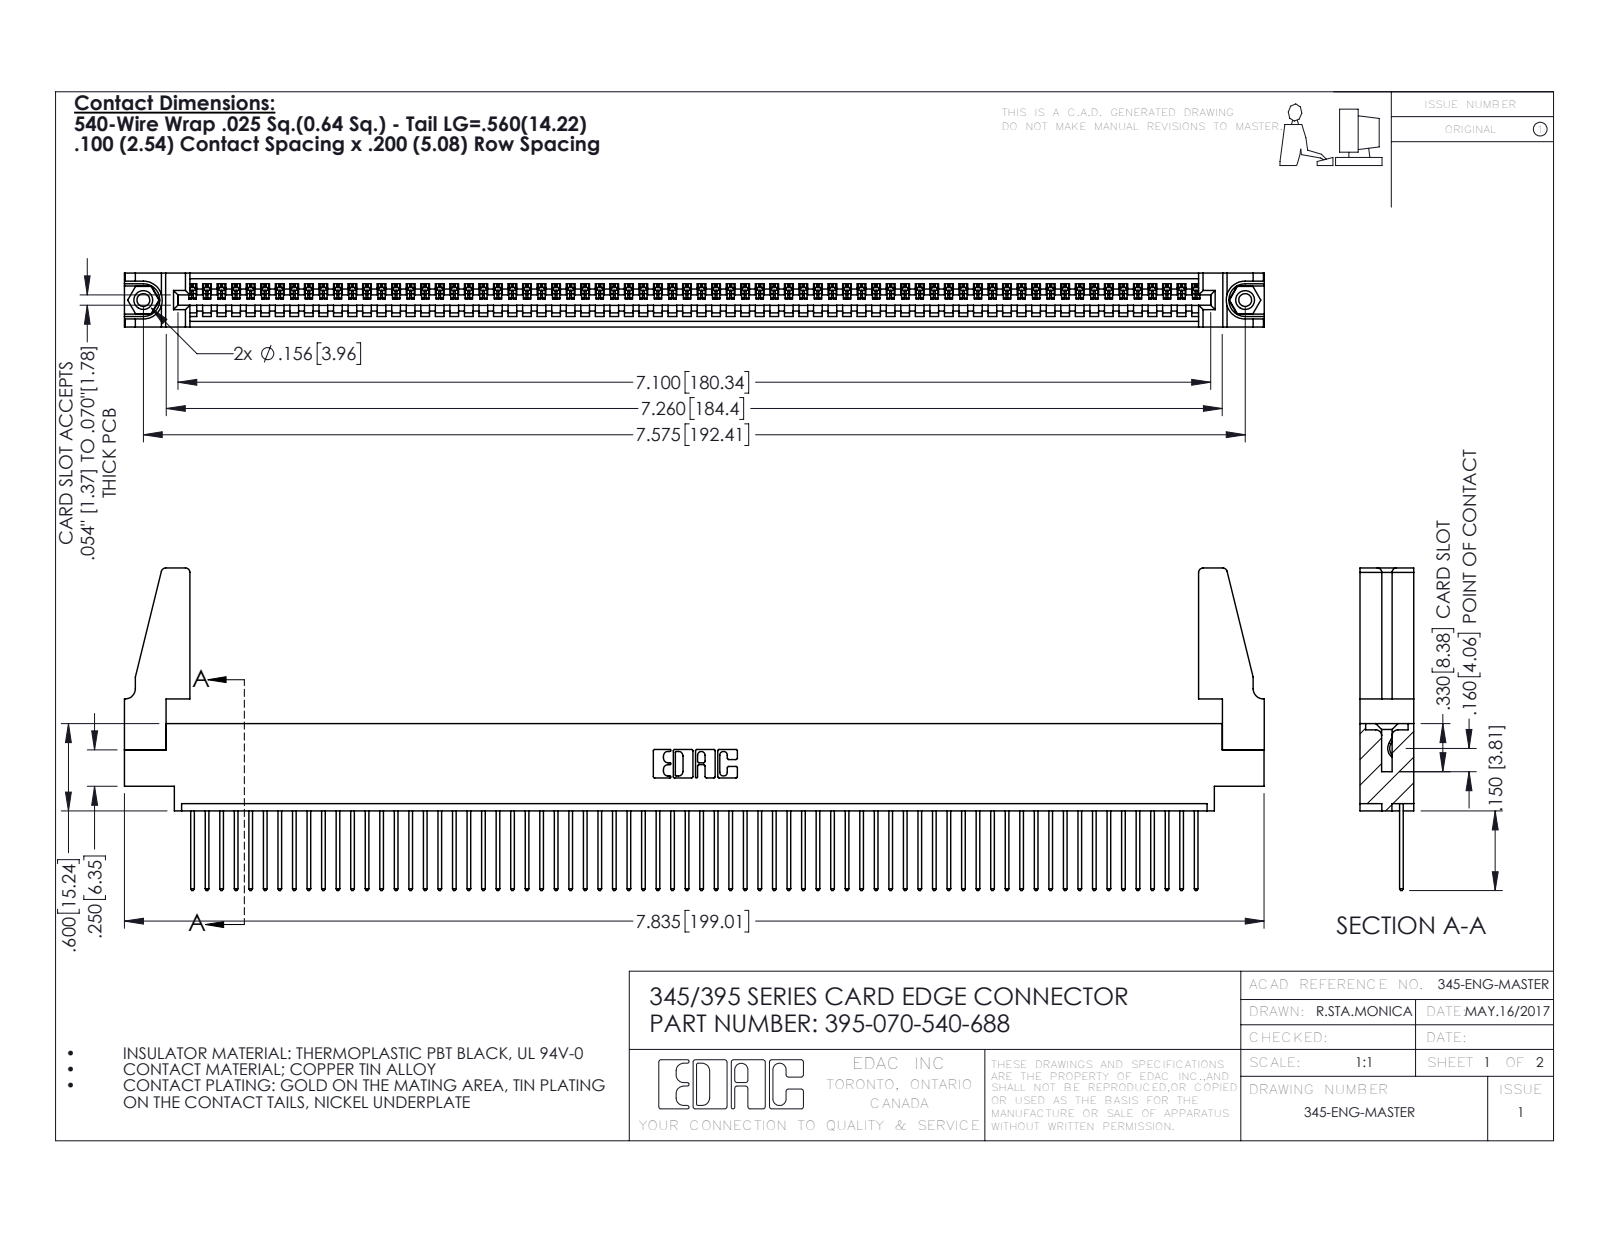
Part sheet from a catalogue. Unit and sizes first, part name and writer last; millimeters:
Units: millimetres
Overall size (bounding box): 199 × 56.3 × 9.4
Round holes (diameter × count): ⌀2.3 ×2, ⌀3.2 ×2, ⌀4 ×2, ⌀1.6 ×1
Round bosses / shafts (diameter × count): ⌀3.9 ×2
Partial cylindrical surfaces — rounded edges, fillets, slot ends (radius × count): R0.2 ×140, R0.3 ×140, R0.3 ×22, R0.8 ×8, R0.2 ×6, R0.8 ×6, R0.7 ×3, R0.8 ×2
Main face-to-face distances: 1.8, 7.6, 9.4, 2.5, 6.9, 0.6, 5.1, 5.7, 4.4, 3.8
Hole centre spacings: 6.9, 186.4, 192.4
Volume: 22 370 mm³ · Surface area: 29 720 mm²
Bodies: 75 solids, 4314 faces (2956 planar, 1342 cylindrical, 16 other)
Part name (STEP PRODUCT): 395-070-540-688; 345-250-001_345-250-001-102; 345-220-078_345-220-088; 345-292-001_345-293-140 (+1 more)
STEP written by: SolidWorks 2016 (CONFIG_CONTROL_DESIGN)
